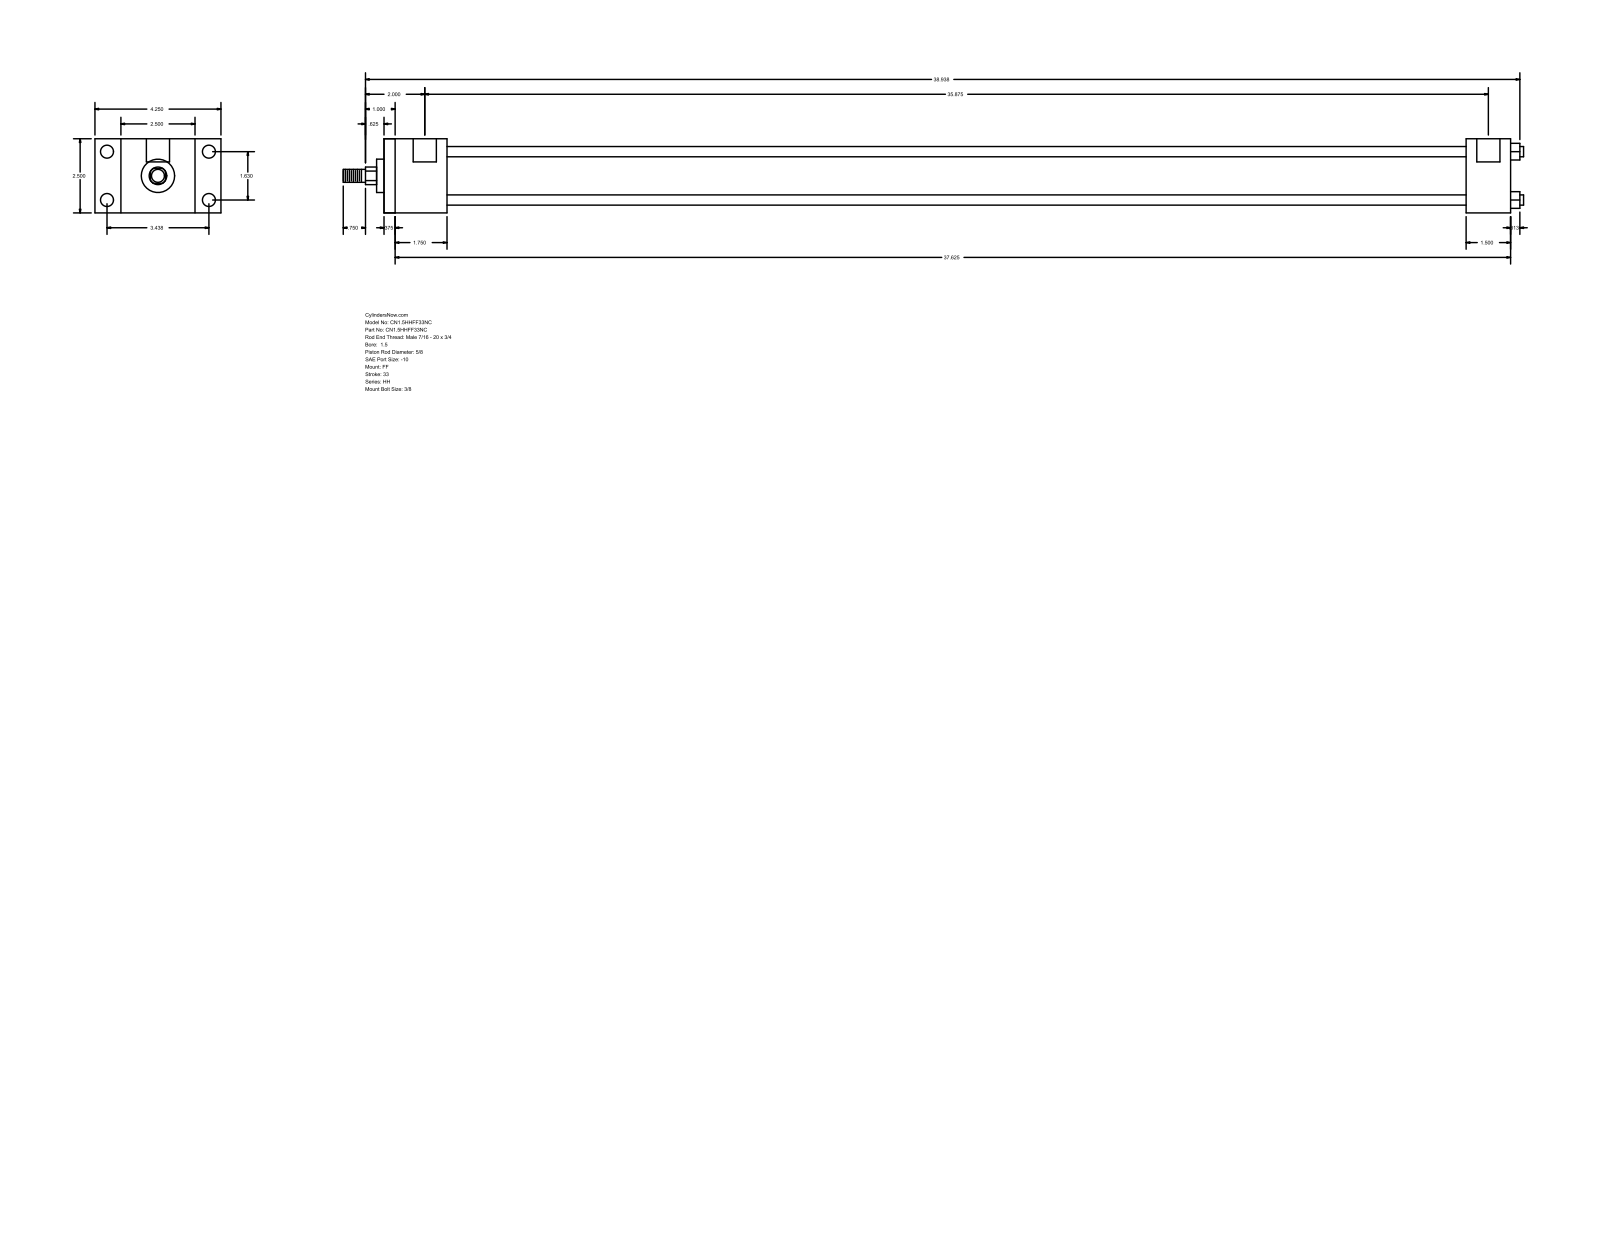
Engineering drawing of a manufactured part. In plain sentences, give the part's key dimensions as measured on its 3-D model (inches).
The part is named "HH_FF__0150_0.625". Its 3-D file was written by "GSSL Pune (CONFIG_CONTROL_DESIGN)". It is 0 solids with 92 faces: 64 planar, 28 cylindrical and 0 other. Overall it measures 39.813 by 4.25 by 2.5 inches. Round holes: 4 of diameter 0.219, 4 of diameter 0.438, 2 of diameter 0.781. Round bosses or shafts: 4 of diameter 0.345, 1 of diameter 1.75, 1 of diameter 1.125, 1 of diameter 0.625, 1 of diameter 0.437. Partial cylindrical surfaces (rounded edges, fillets, slot ends): 1 of radius 0.297. The main face-to-face distances are 2.5, 38, 1.5, 0.375, 37.625, 1.75, 2.125, 35.875, 36.5, 36.125. The hole center spacings are 0.063, 1.63, 3.438, 3.805, 35.937, 36, 35.875.
